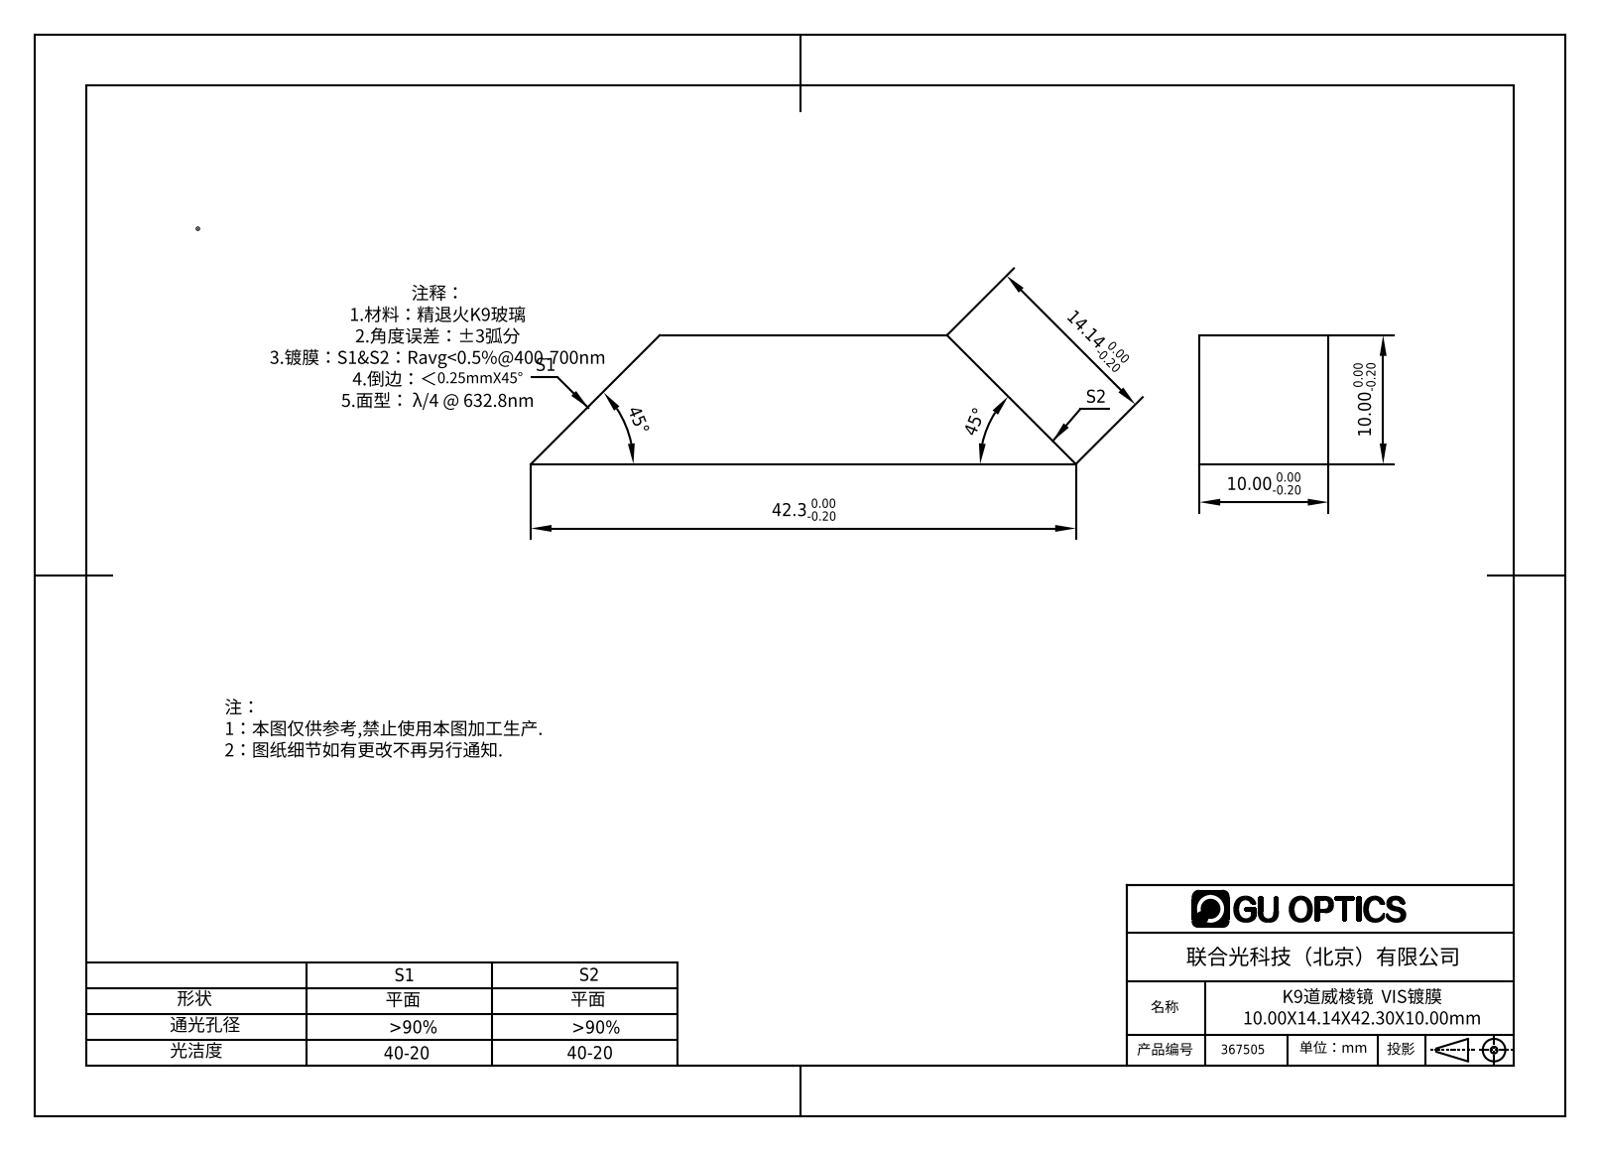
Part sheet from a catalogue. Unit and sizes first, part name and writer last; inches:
Units: inches
Overall size (bounding box): 1.665 × 0.394 × 0.394
Main face-to-face distances: 0.394
Volume: 0.197 in³ · Surface area: 2.441 in²
Bodies: 1 solid, 6 faces (6 planar, 0 cylindrical, 0 other)
Part name (STEP PRODUCT): 367501
STEP written by: SolidWorks 2016 (CONFIG_CONTROL_DESIGN)
